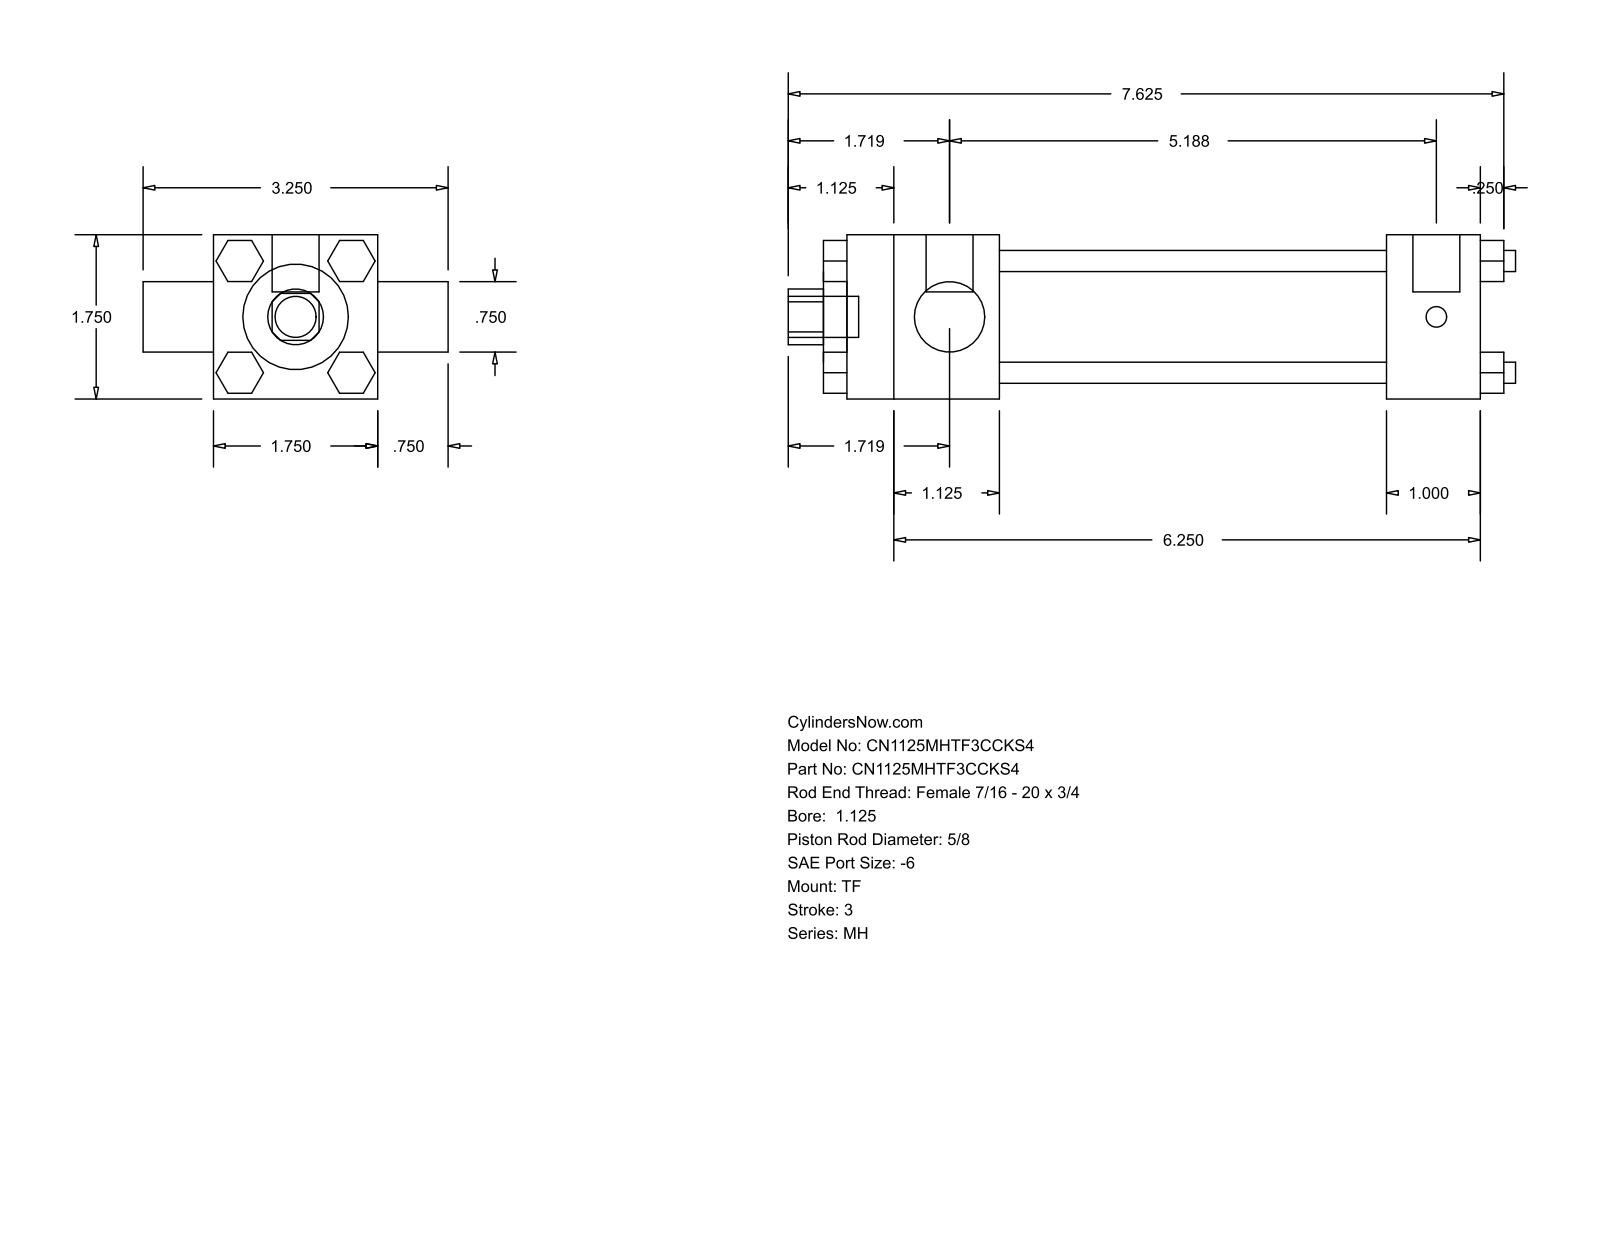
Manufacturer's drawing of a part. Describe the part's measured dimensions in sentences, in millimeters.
The part is named "MH_TF__0112_0.625". Its 3-D file was written by "GSSL Pune (CONFIG_CONTROL_DESIGN)". It is 0 solids with 120 faces: 92 planar, 28 cylindrical and 0 other. Overall it measures 196.85 by 82.55 by 44.45 millimeters. Round holes: 1 of diameter 15.88, 1 of diameter 19.05, 1 of diameter 28.57, 1 of diameter 34.92. Round bosses or shafts: 4 of diameter 5.71, 3 of diameter 5.56, 2 of diameter 12.7, 1 of diameter 11.11. Partial cylindrical surfaces (rounded edges, fillets, slot ends): 1 of radius 7.54. The main face-to-face distances are 44.46, 11.11, 104.78, 130.17, 25.39, 41.27, 146.05, 171.44, 47.62, 6.35.
